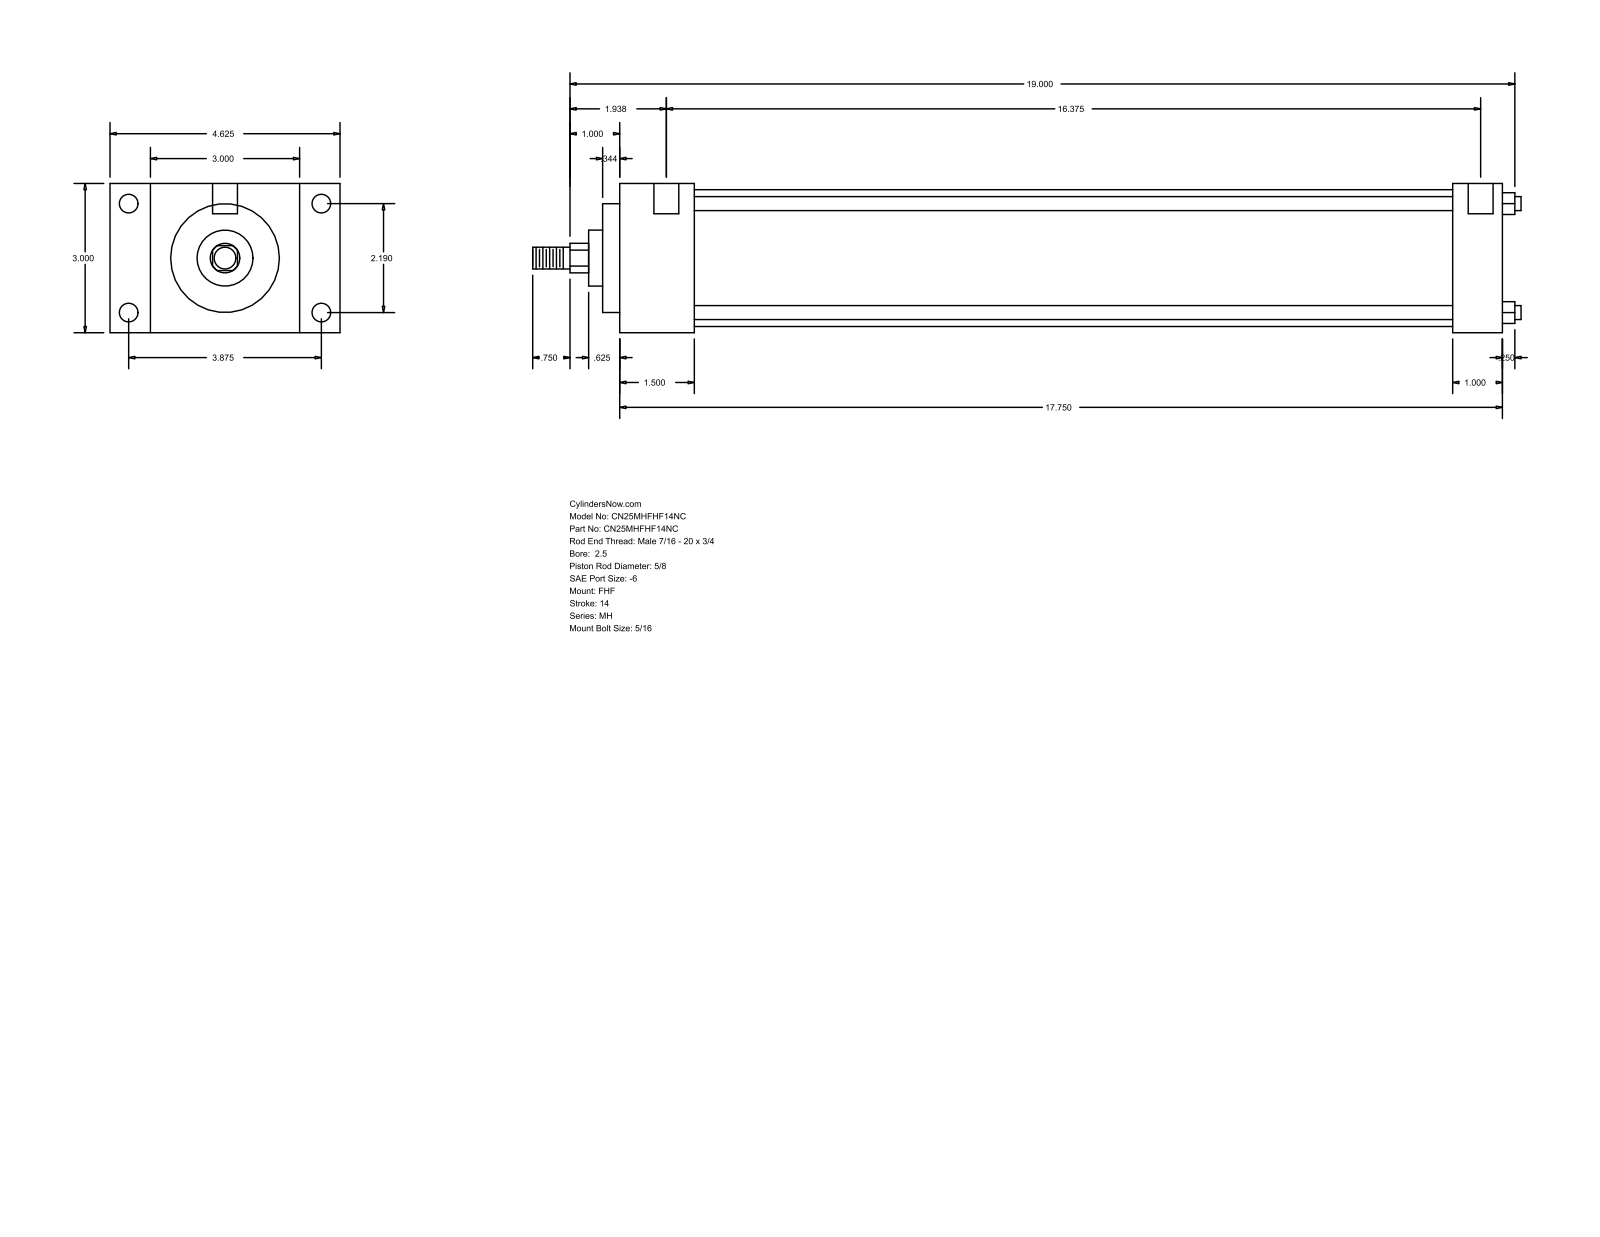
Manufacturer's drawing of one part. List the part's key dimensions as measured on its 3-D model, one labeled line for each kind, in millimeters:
Part name (STEP PRODUCT): MH_FHF__0250_0.625
STEP written by: GSSL Pune (CONFIG_CONTROL_DESIGN)
Units: millimetres
Bodies: 0 solids, 90 faces (61 planar, 29 cylindrical, 0 other)
Overall size (bounding box): 504.82 × 117.47 × 76.2
Round holes (diameter × count): ⌀5.56 ×4, ⌀9.53 ×4, ⌀12.7 ×2
Round bosses / shafts (diameter × count): ⌀7.14 ×4, ⌀69.85 ×1, ⌀55.55 ×1, ⌀28.57 ×1, ⌀15.88 ×1, ⌀11.11 ×1
Partial cylindrical surfaces — rounded edges, fillets, slot ends (radius × count): R7.54 ×1
Main face-to-face distances: 76.2, 450.85, 38.1, 412.75, 20.64, 96.84, 117.48, 25.4, 425.45, 387.35
Hole centre spacings: 55.62, 98.42, 113.05, 423.86, 3.17, 4.76, 415.93, 419.1
